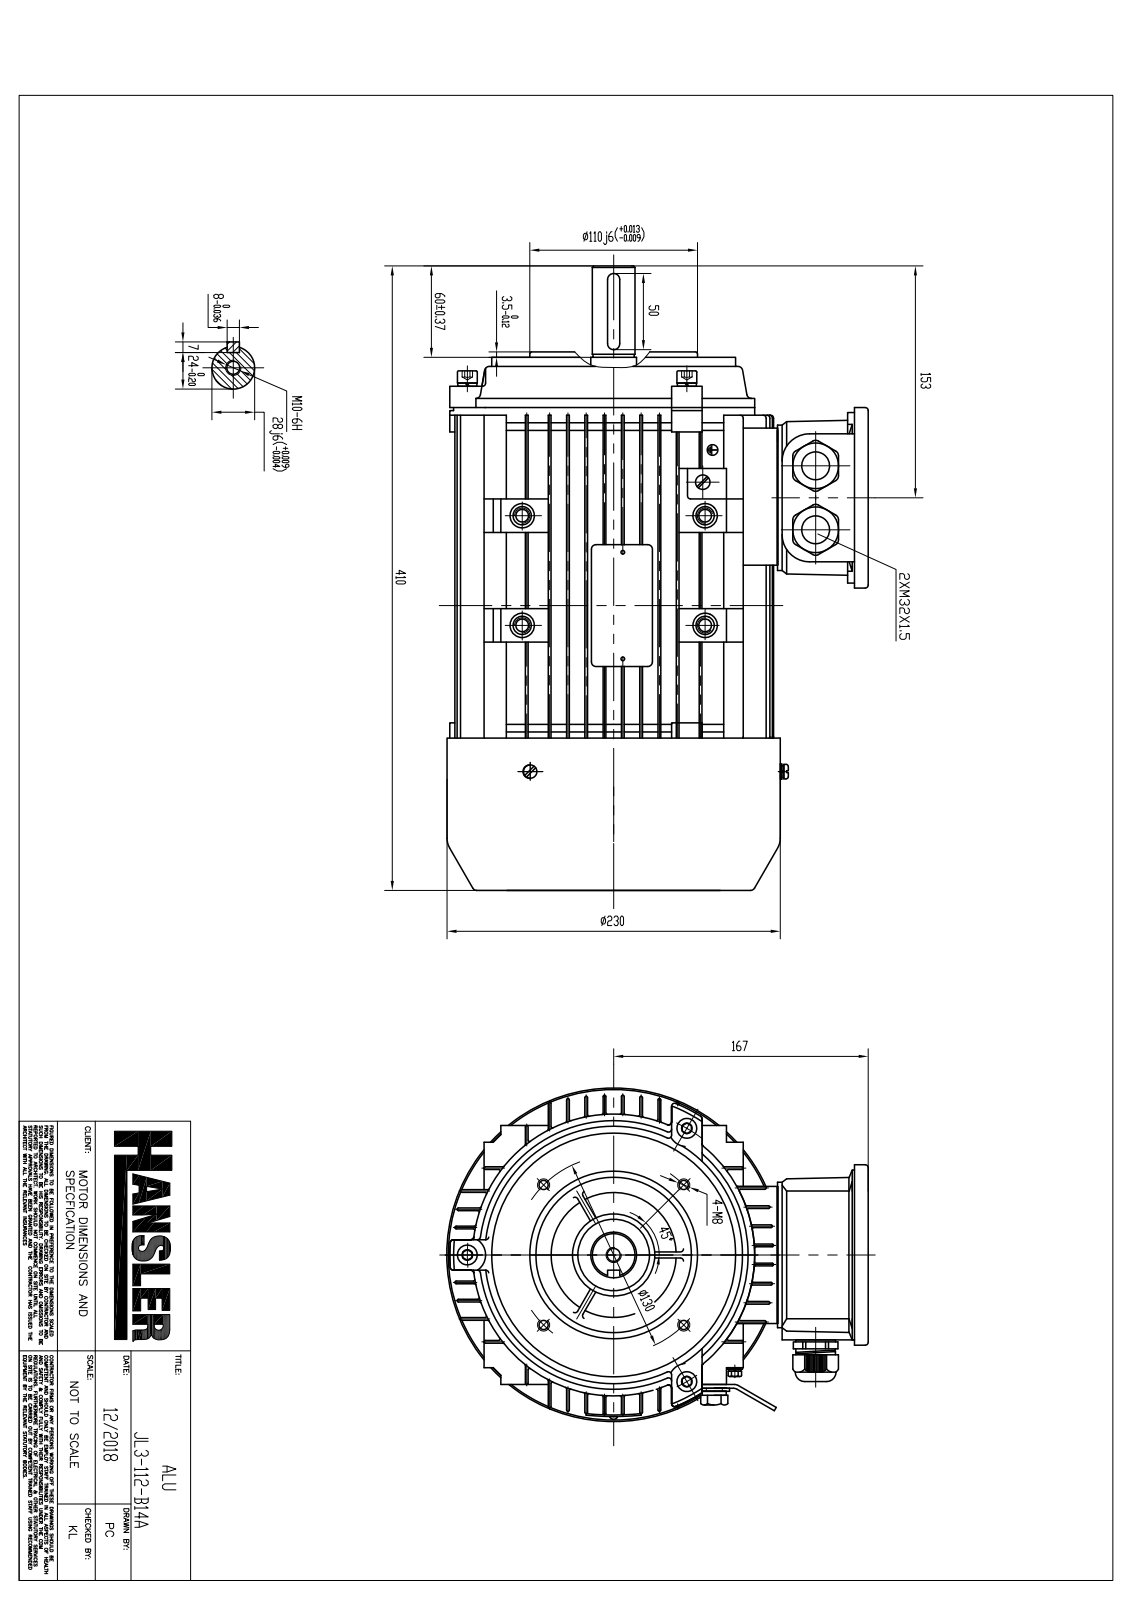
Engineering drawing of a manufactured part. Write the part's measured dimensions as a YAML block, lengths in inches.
part_name: "JL3-112-B14A"
step_written_by: "SolidWorks 2018 (CONFIG_CONTROL_DESIGN)"
units: inches
bodies: {solids: 49, faces: 4033, planar: 1651, cylindrical: 1688, other: 694}
overall_size: [15.551, 11.286, 9.422]
volume: 158.5
surface_area: 1837
round_holes:
  - {diameter: 0.315, count: 16}
  - {diameter: 0.228, count: 10}
  - {diameter: 0.709, count: 8}
  - {diameter: 0.197, count: 6}
  - {diameter: 0.157, count: 4}
  - {diameter: 0.207, count: 4}
  - {diameter: 0.209, count: 4}
  - {diameter: 0.394, count: 4}
  - {diameter: 0.152, count: 3}
  - {diameter: 0.33, count: 3}
  - {diameter: 0.338, count: 2}
  - {diameter: 0.433, count: 2}
round_bosses_or_shafts:
  - {diameter: 0.591, count: 8}
  - {diameter: 0.472, count: 8}
  - {diameter: 0.197, count: 8}
  - {diameter: 0.394, count: 4}
  - {diameter: 0.374, count: 4}
  - {diameter: 0.309, count: 4}
  - {diameter: 0.176, count: 4}
  - {diameter: 0.496, count: 3}
partial_cylinders:
  - {radius: 0.02, count: 656}
  - {radius: 0.039, count: 78}
  - {radius: 0.079, count: 32}
  - {radius: 0.118, count: 23}
  - {radius: 0.157, count: 20}
  - {radius: 0.197, count: 17}
  - {radius: 0.012, count: 16}
  - {radius: 0.008, count: 12}
face_to_face_distances: [0.071, 0.591, 3.937, 0.551, 3.346, 0.661, 2.795, 4.528, 1.102, 1.654]
hole_center_spacings: [3.32, 3.858, 0.837, 1.727, 0.056, 0.709, 0.817, 0.835]
